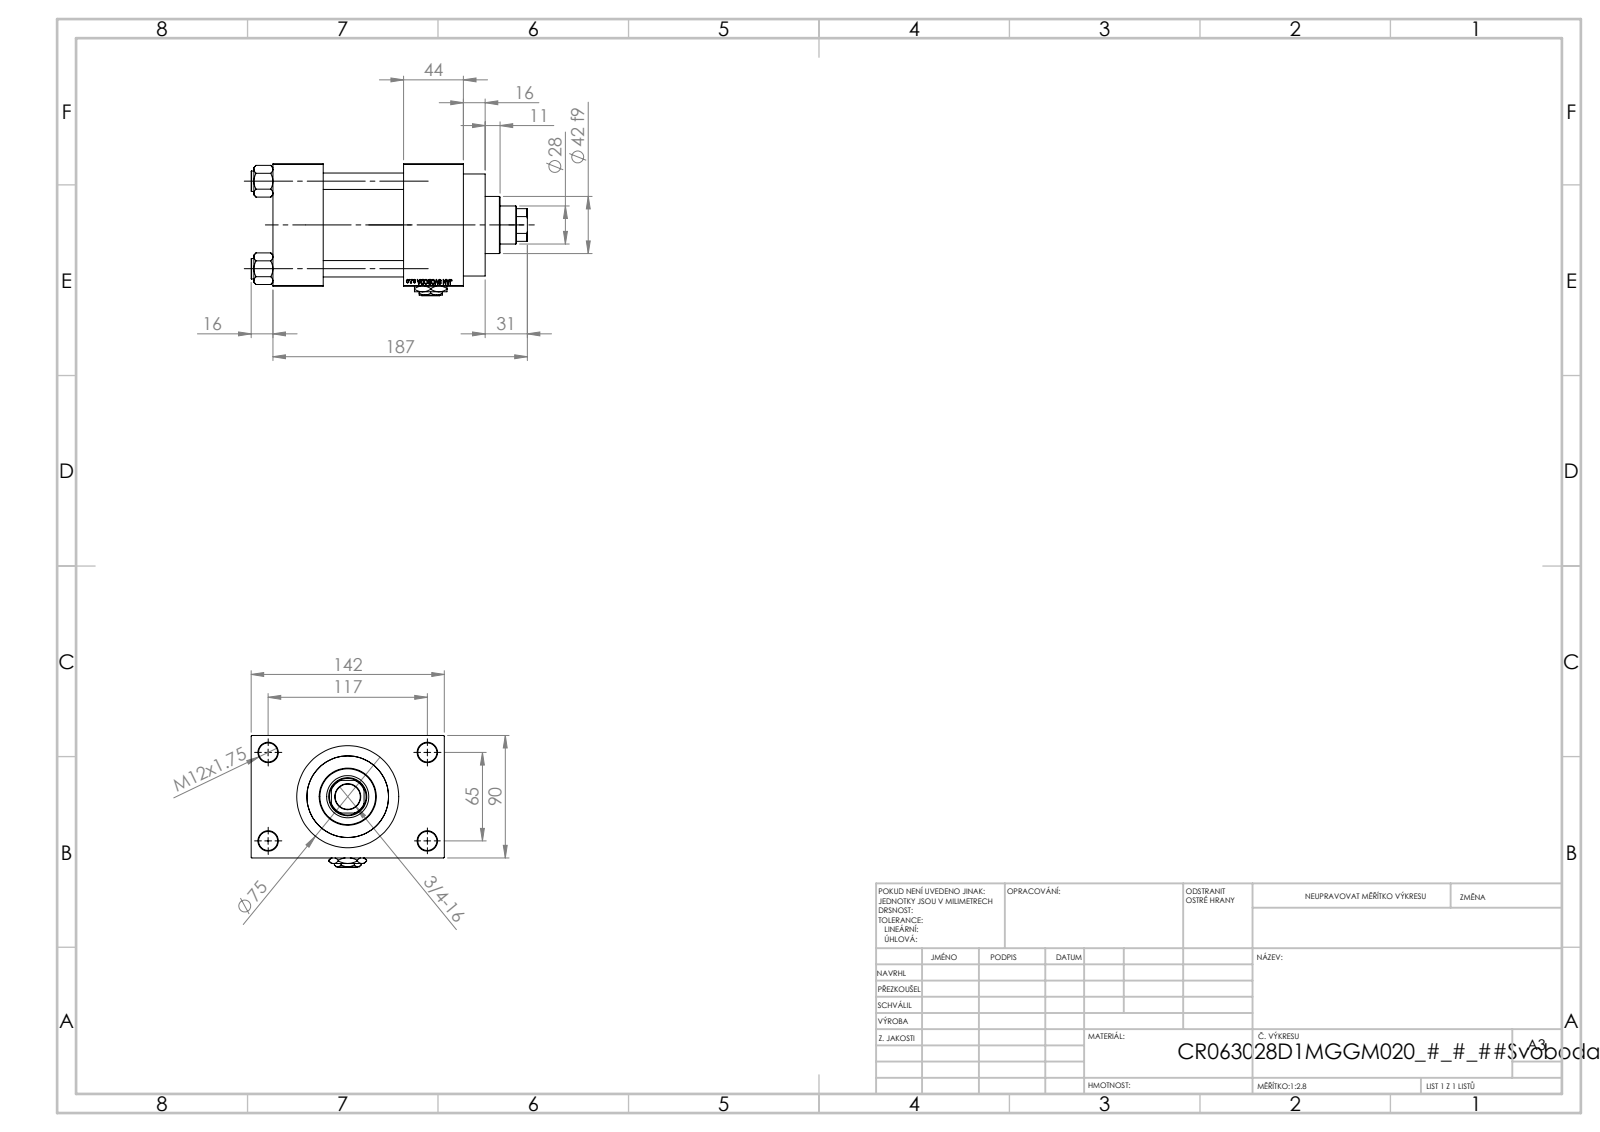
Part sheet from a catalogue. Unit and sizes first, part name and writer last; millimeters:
Units: millimetres
Overall size (bounding box): 203 × 142 × 97
Round holes (diameter × count): ⌀12 ×4, ⌀14 ×4, ⌀7 ×2, ⌀20.96 ×2, ⌀30 ×2, ⌀18.5 ×1, ⌀28 ×1, ⌀31 ×1, ⌀50 ×1, ⌀60 ×1, ⌀63 ×1
Round bosses / shafts (diameter × count): ⌀15 ×4, ⌀75 ×1, ⌀69 ×1, ⌀42 ×1
Partial cylindrical surfaces — rounded edges, fillets, slot ends (radius × count): R13.5 ×1
Main face-to-face distances: 90, 59, 37, 96, 140, 103, 44, 26, 116, 142
Hole centre spacings: 26.35, 45.47, 64.3, 66.92, 69.81, 90.65, 111.34, 65
Volume: 1 102 000 mm³ · Surface area: 200 463 mm²
Bodies: 12 solids, 1152 faces (521 planar, 93 cylindrical, 538 other)
Part name (STEP PRODUCT): V215CR_D_Body; NUT_M5_D; V215_VC_A; Zatka_pro_OIL_PORT (+2 more)
STEP written by: SolidWorks 2019 (CONFIG_CONTROL_DESIGN)
